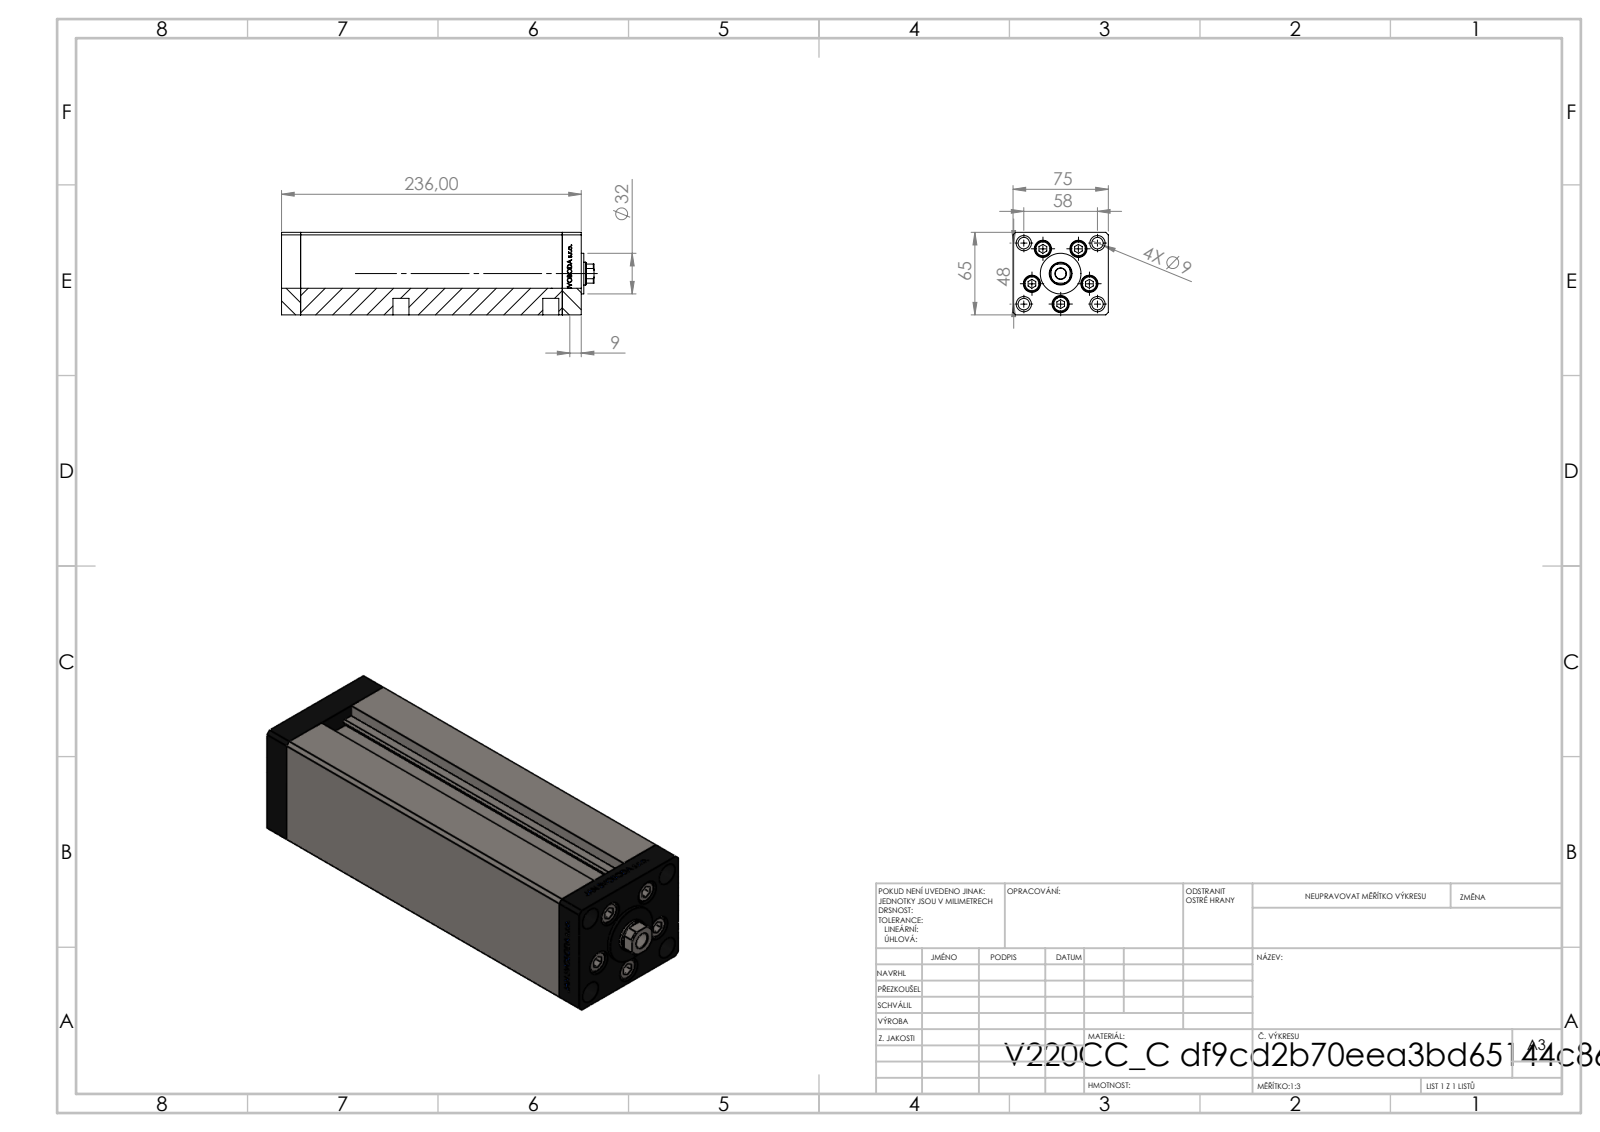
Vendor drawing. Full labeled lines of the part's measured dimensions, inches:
Part name (STEP PRODUCT): V220C_VC_C; V220C FRONT; V220C BACK_C; ALLEN BOLT (+1 more)
STEP written by: SolidWorks 2019 (CONFIG_CONTROL_DESIGN)
Units: inches
Bodies: 13 solids, 1183 faces (546 planar, 175 cylindrical, 462 other)
Overall size (bounding box): 9.685 × 2.953 × 2.559
Volume: 58.49 in³ · Surface area: 278 in²
Round holes (diameter × count): ⌀0.354 ×9, ⌀0.531 ×5, ⌀0.079 ×4, ⌀0.315 ×4, ⌀0.472 ×4, ⌀0.518 ×4, ⌀0.335 ×1, ⌀0.492 ×1, ⌀0.709 ×1
Round bosses / shafts (diameter × count): ⌀0.315 ×5, ⌀0.492 ×4, ⌀1.26 ×1
Partial cylindrical surfaces — rounded edges, fillets, slot ends (radius × count): R0.037 ×2, R0.335 ×1
Main face-to-face distances: 2.953, 2.559, 0.591, 8.11, 8.701, 9.291, 2.146, 0.413, 1.033, 1.919
Hole centre spacings: 0.945, 1.482, 0.617, 0.678, 1.091, 1.135, 1.142, 1.285
